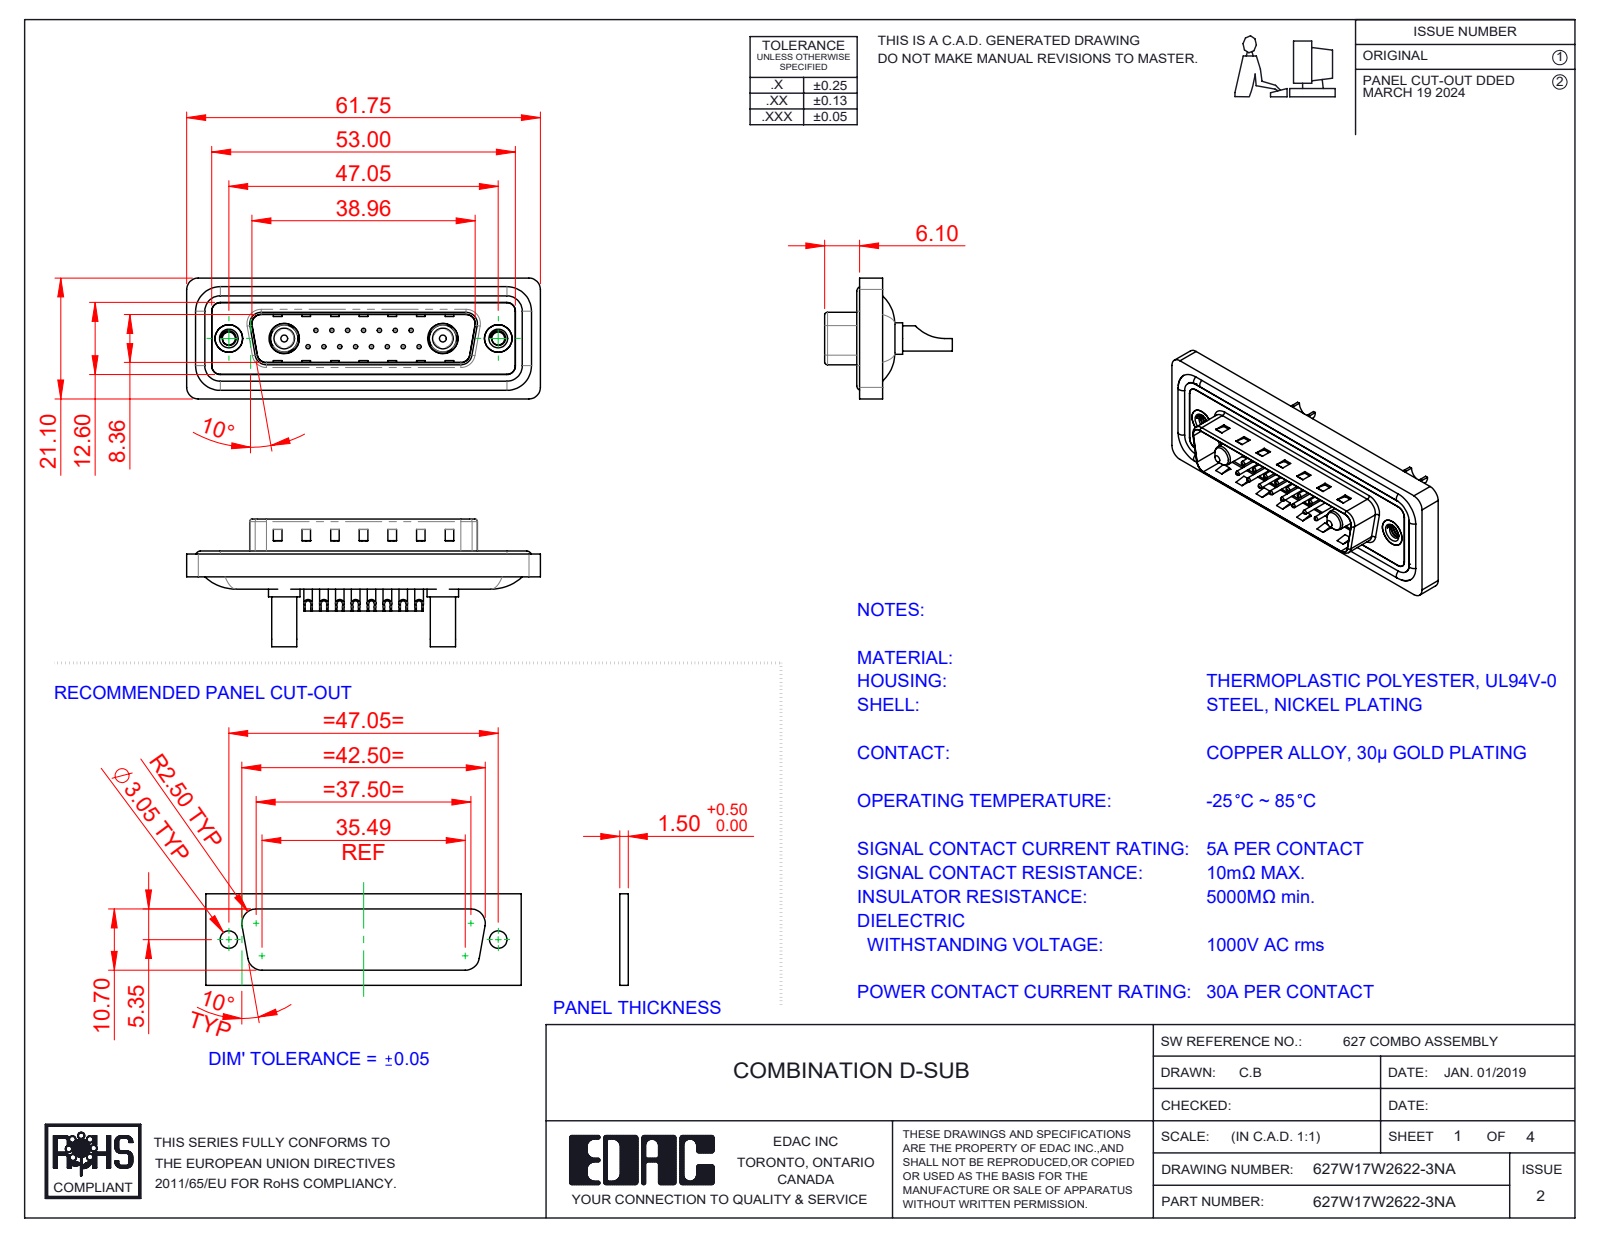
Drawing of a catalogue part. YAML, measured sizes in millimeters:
part_name: "627Combo Threaded Rivet_A; Power Pin_30A SC; 627Combo Shell Front_25 Contacts; 627Combo Waterproof Housing_25 Contacts (+5 more)"
step_written_by: "SolidWorks 2023 (CONFIG_CONTROL_DESIGN)"
units: millimeters
bodies: {solids: 26, faces: 1126, planar: 370, cylindrical: 474, other: 282}
overall_size: [61.75, 22.3, 21.1]
volume: 7339
surface_area: 12246
round_holes:
  - {diameter: 0.75, count: 15}
  - {diameter: 1, count: 15}
  - {diameter: 1.6, count: 15}
  - {diameter: 2, count: 15}
  - {diameter: 2.26, count: 2}
  - {diameter: 3.5, count: 2}
  - {diameter: 4, count: 2}
  - {diameter: 4.8, count: 2}
  - {diameter: 4.85, count: 2}
  - {diameter: 5, count: 2}
  - {diameter: 5.3, count: 2}
round_bosses_or_shafts:
  - {diameter: 1.5, count: 15}
  - {diameter: 1.6, count: 4}
  - {diameter: 5.5, count: 2}
  - {diameter: 5.2, count: 2}
  - {diameter: 4.9, count: 2}
  - {diameter: 4.75, count: 2}
  - {diameter: 4.4, count: 2}
  - {diameter: 3.75, count: 2}
partial_cylinders:
  - {radius: 1.5, count: 22}
  - {radius: 2, count: 18}
  - {radius: 0.5, count: 8}
  - {radius: 1.6, count: 8}
  - {radius: 1, count: 6}
  - {radius: 0.25, count: 4}
  - {radius: 0.6, count: 4}
  - {radius: 0.65, count: 4}
face_to_face_distances: [0.4, 1.5, 1.1, 1.6, 0.5, 3.1, 2.9, 0.82, 9.58, 4.1]
hole_center_spacings: [3.16, 2.77, 5.54, 8.31, 5.04, 7.49, 11.08, 5.03]
